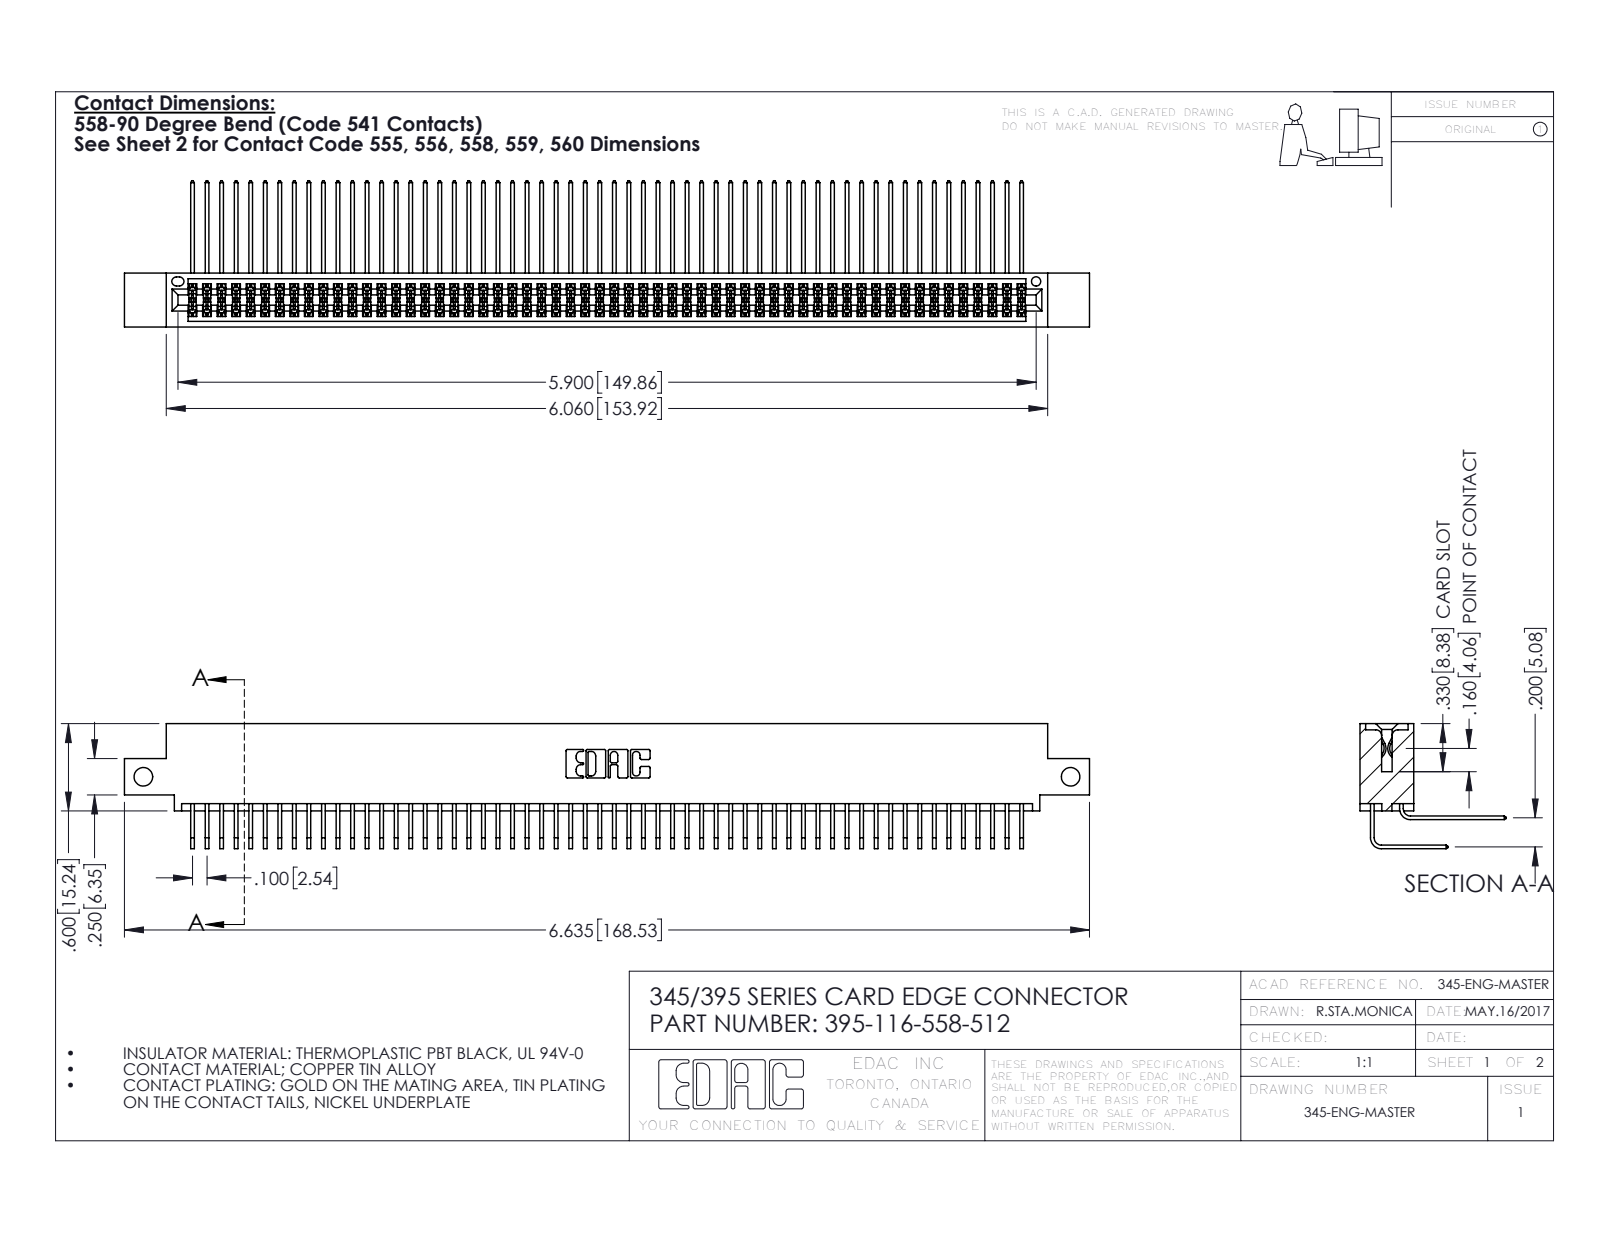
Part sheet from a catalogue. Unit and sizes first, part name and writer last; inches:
Units: inches
Overall size (bounding box): 6.635 × 1.005 × 0.859
Round holes (diameter × count): ⌀0.128 ×2, ⌀0.064 ×1
Partial cylindrical surfaces — rounded edges, fillets, slot ends (radius × count): R0.006 ×174, R0.01 ×22, R0.007 ×6, R0.031 ×6, R0.026 ×3, R0.014 ×2, R0.019 ×2, R0.022 ×2
Main face-to-face distances: 0.072, 0.298, 0.2, 0.37, 0.098, 0.272, 0.025, 0.225, 0.025, 0.175
Hole centre spacings: 6.375
Volume: 1.039 in³ · Surface area: 44.31 in²
Bodies: 117 solids, 6162 faces (4144 planar, 2018 cylindrical, 0 other)
Part name (STEP PRODUCT): 345-292-001_558 559 Tail - 1; 345-292-001_558 Tail - 2; 345 Part_0.110 Offset - Side Mount; 395-116-558-512
STEP written by: SolidWorks 2016 (CONFIG_CONTROL_DESIGN)
